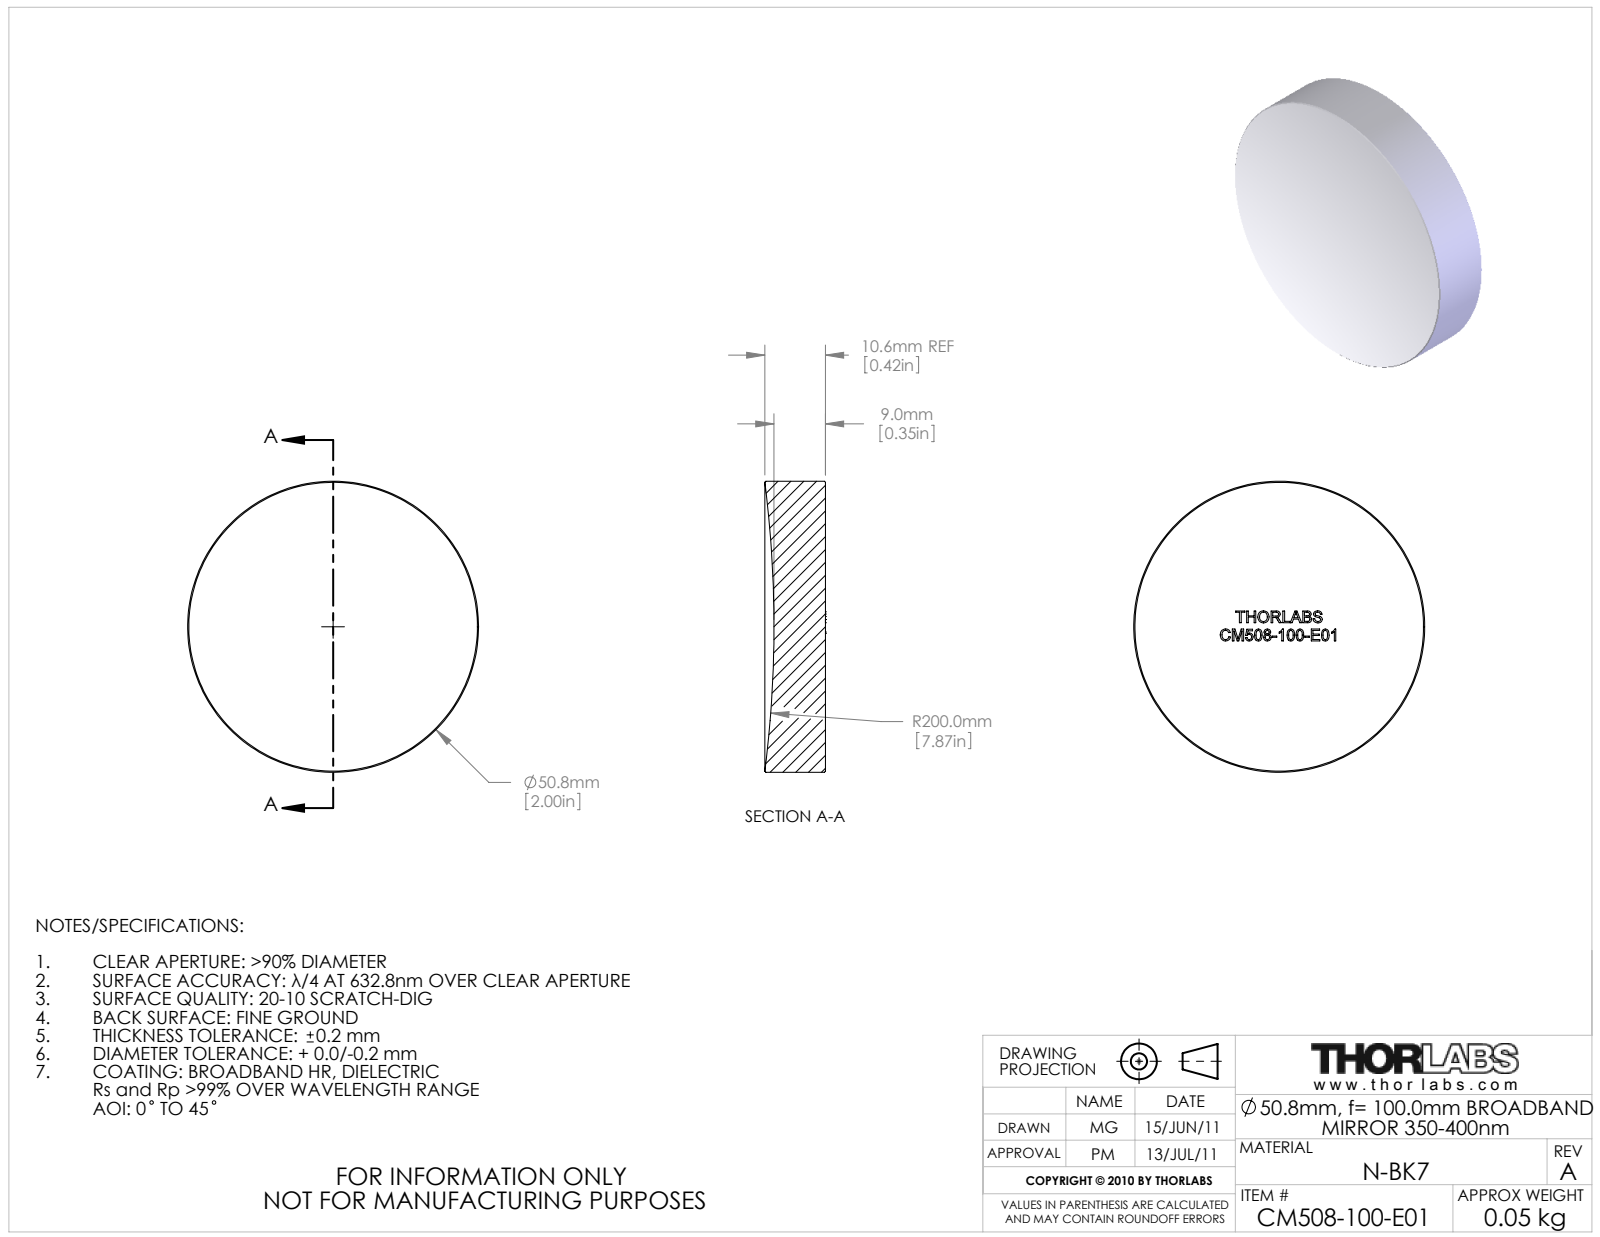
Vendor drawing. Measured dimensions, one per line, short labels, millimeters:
name: 22616-E0W
written by: SolidWorks 2011 (AUTOMOTIVE_DESIGN)
unit: mm
bodies: 0 solids, 42 faces (34 planar, 2 cylindrical, 6 other)
size: 50.8 × 50.8 × 10.59
bosses: 1× ⌀50.8
